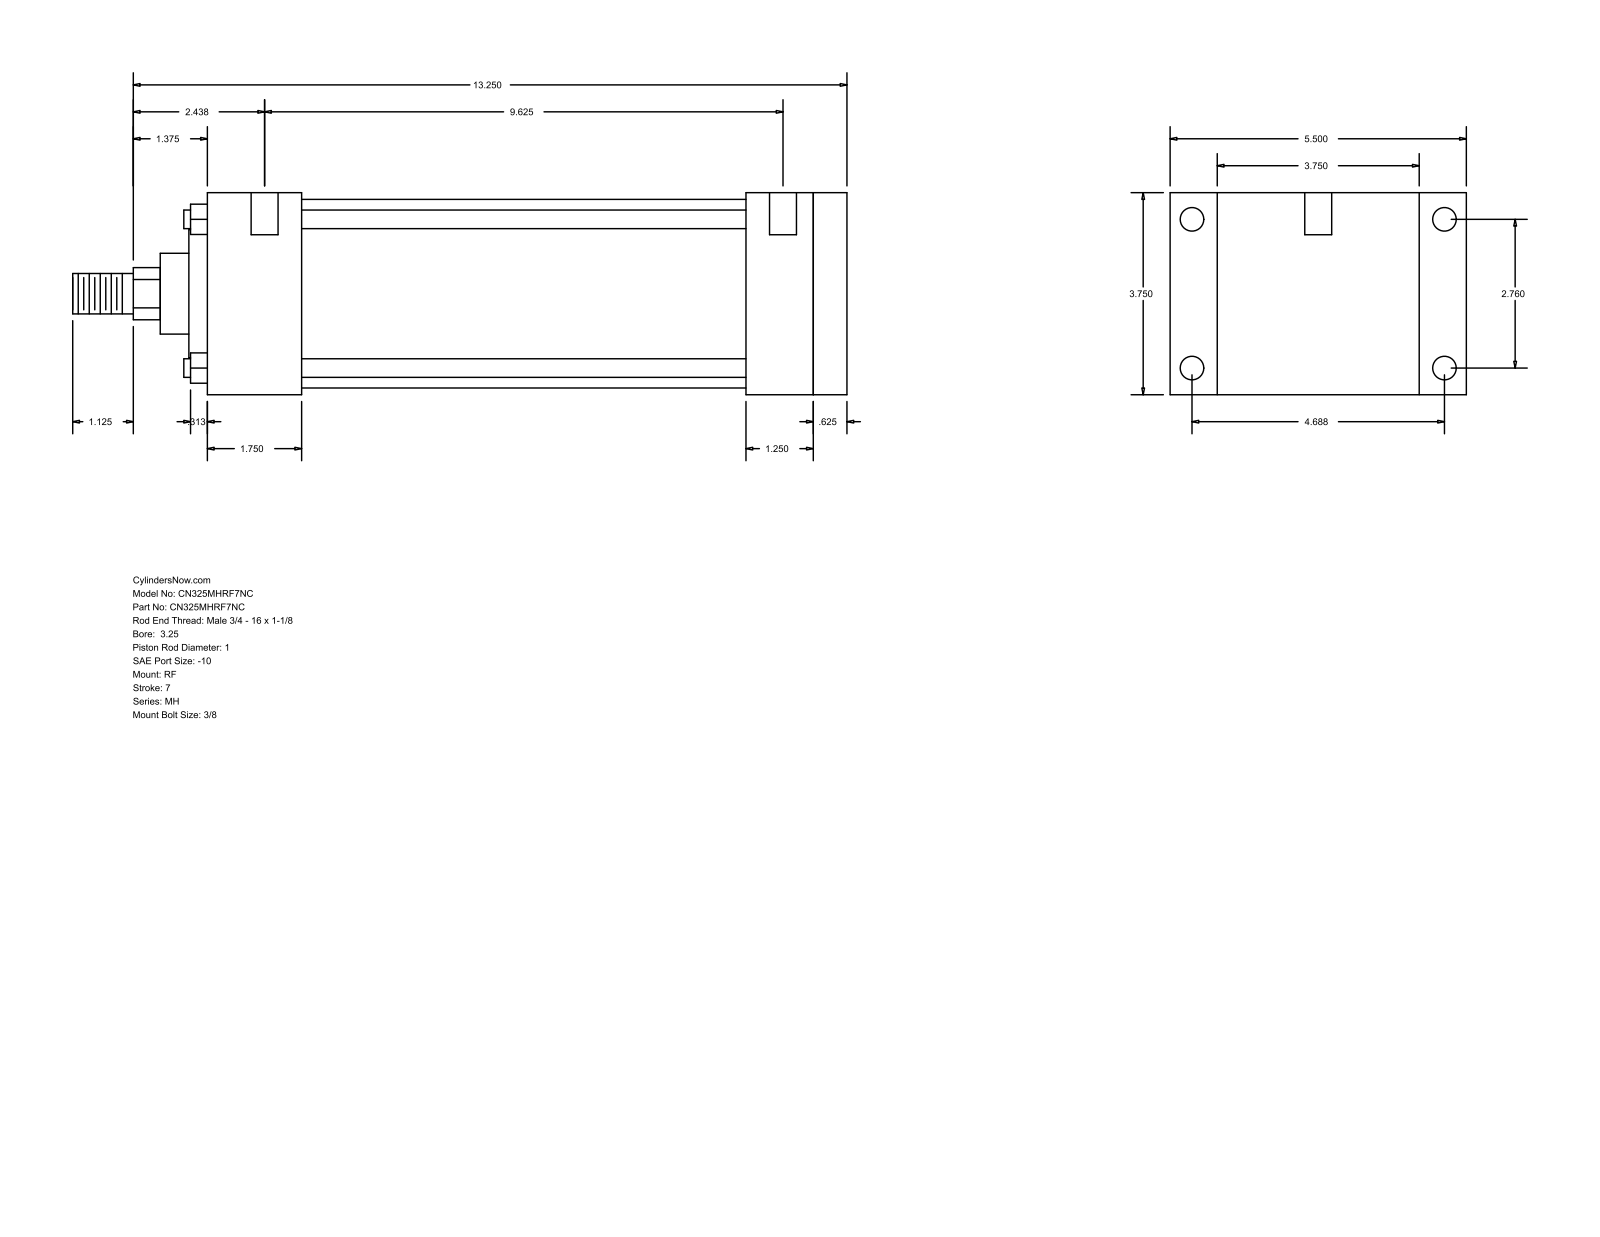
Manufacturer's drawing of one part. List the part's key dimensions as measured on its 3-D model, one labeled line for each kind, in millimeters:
Part name (STEP PRODUCT): MH_RF__0325_1
STEP written by: GSSL Pune (CONFIG_CONTROL_DESIGN)
Units: millimetres
Bodies: 0 solids, 94 faces (65 planar, 29 cylindrical, 0 other)
Overall size (bounding box): 365.12 × 139.7 × 95.25
Round holes (diameter × count): ⌀5.56 ×4, ⌀11.13 ×4, ⌀12.7 ×2
Round bosses / shafts (diameter × count): ⌀8.76 ×4, ⌀88.9 ×1, ⌀60.33 ×1, ⌀38.1 ×1, ⌀25.4 ×1, ⌀19.05 ×1
Partial cylindrical surfaces — rounded edges, fillets, slot ends (radius × count): R12.29 ×1
Main face-to-face distances: 95.24, 301.63, 285.76, 15.87, 22.23, 117.47, 44.46, 241.3, 257.17, 254.01
Hole centre spacings: 70.1, 119.06, 138.16, 250.82, 1.58, 4.76, 244.48, 246.06
